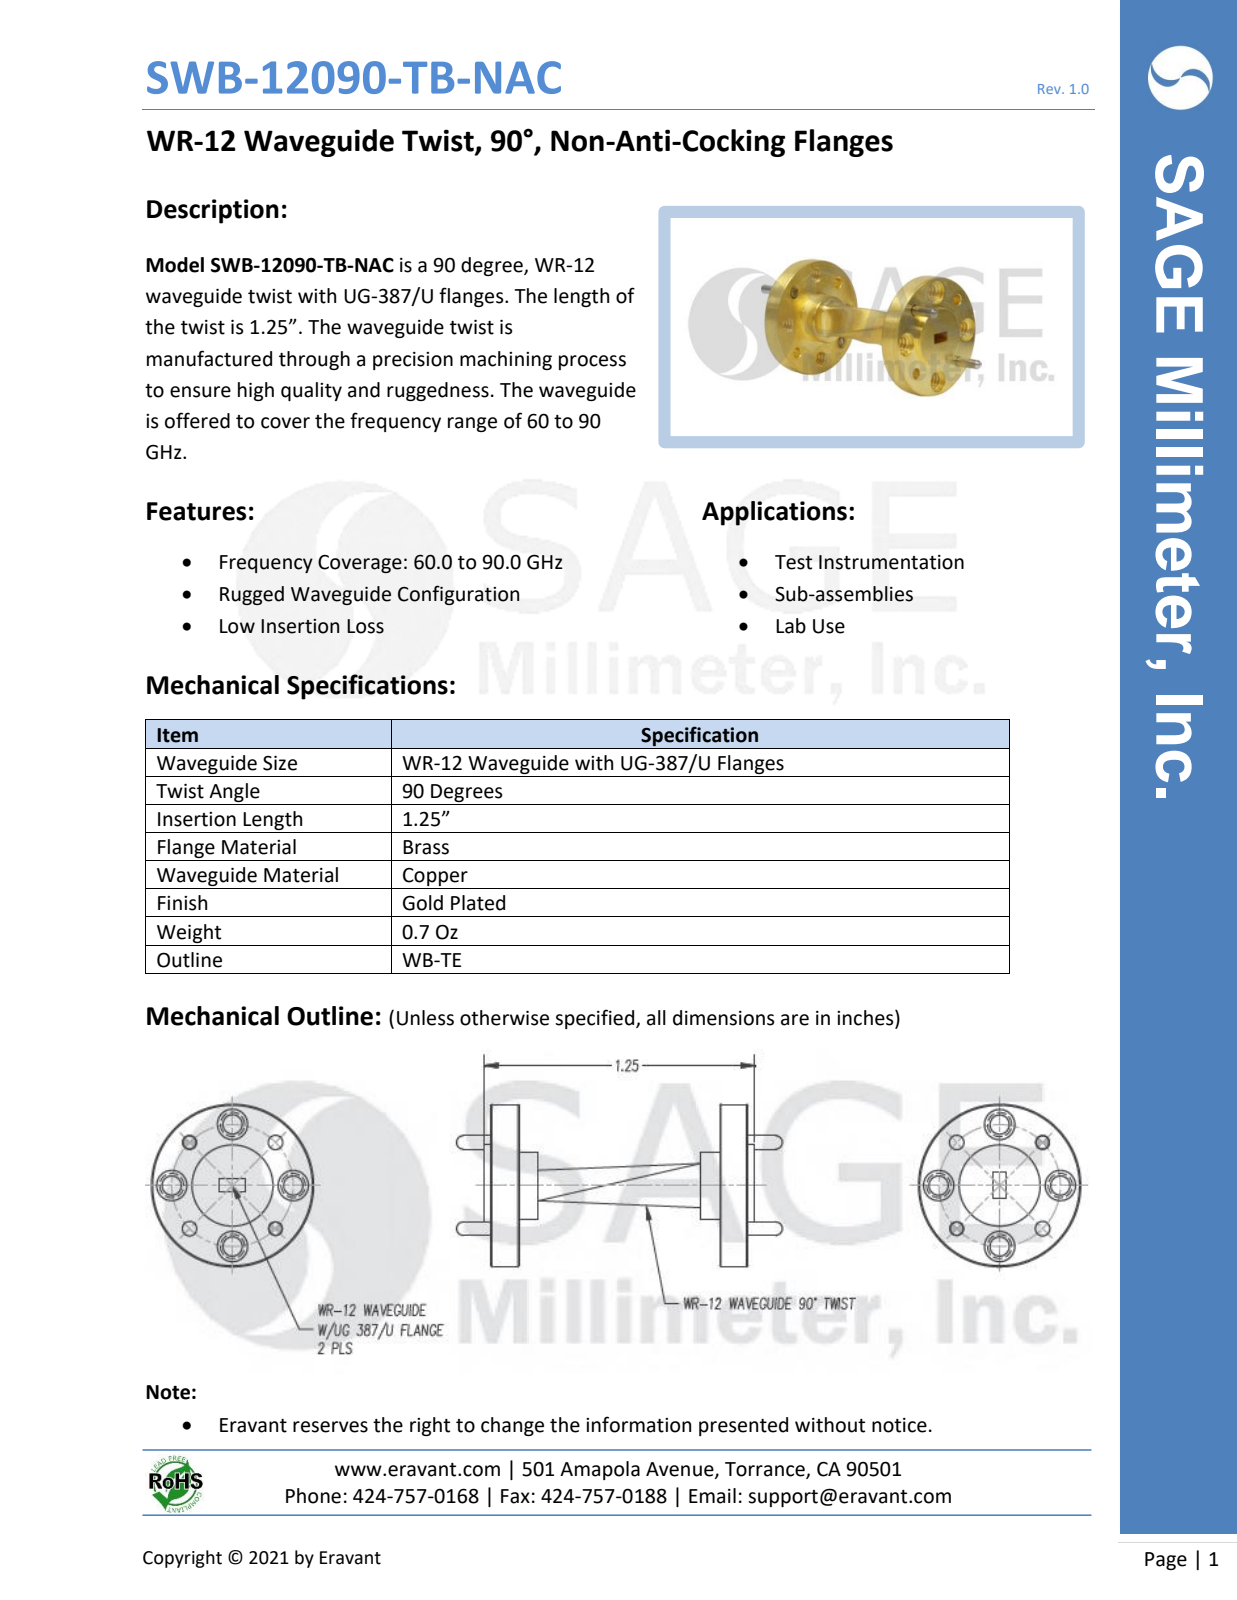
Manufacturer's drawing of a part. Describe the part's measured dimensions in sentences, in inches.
The part is named "WB-TE". Its 3-D file was written by "SolidWorks 2021 (AUTOMOTIVE_DESIGN)". It is 5 solids with 146 faces: 34 planar, 68 cylindrical and 44 other. Overall it measures 1.555 by 0.75 by 0.75 inches. Its volume is 0.141 cubic inches and its surface area 3.572 square inches. Round holes: 4 of diameter 0.06, 4 of diameter 0.067, 4 of diameter 0.089, 4 of diameter 0.14. Round bosses or shafts: 2 of diameter 0.063, 1 of diameter 0.75, 1 of diameter 0.375, 1 of diameter 0.31. The main face-to-face distances are 0.93, 1.19, 0.13, 1.06, 1.06, 0.13, 0.03, 1.22, 0.16, 1.09. The hole center spacings are 0.215, 0.398, 0.519, 0.562.
